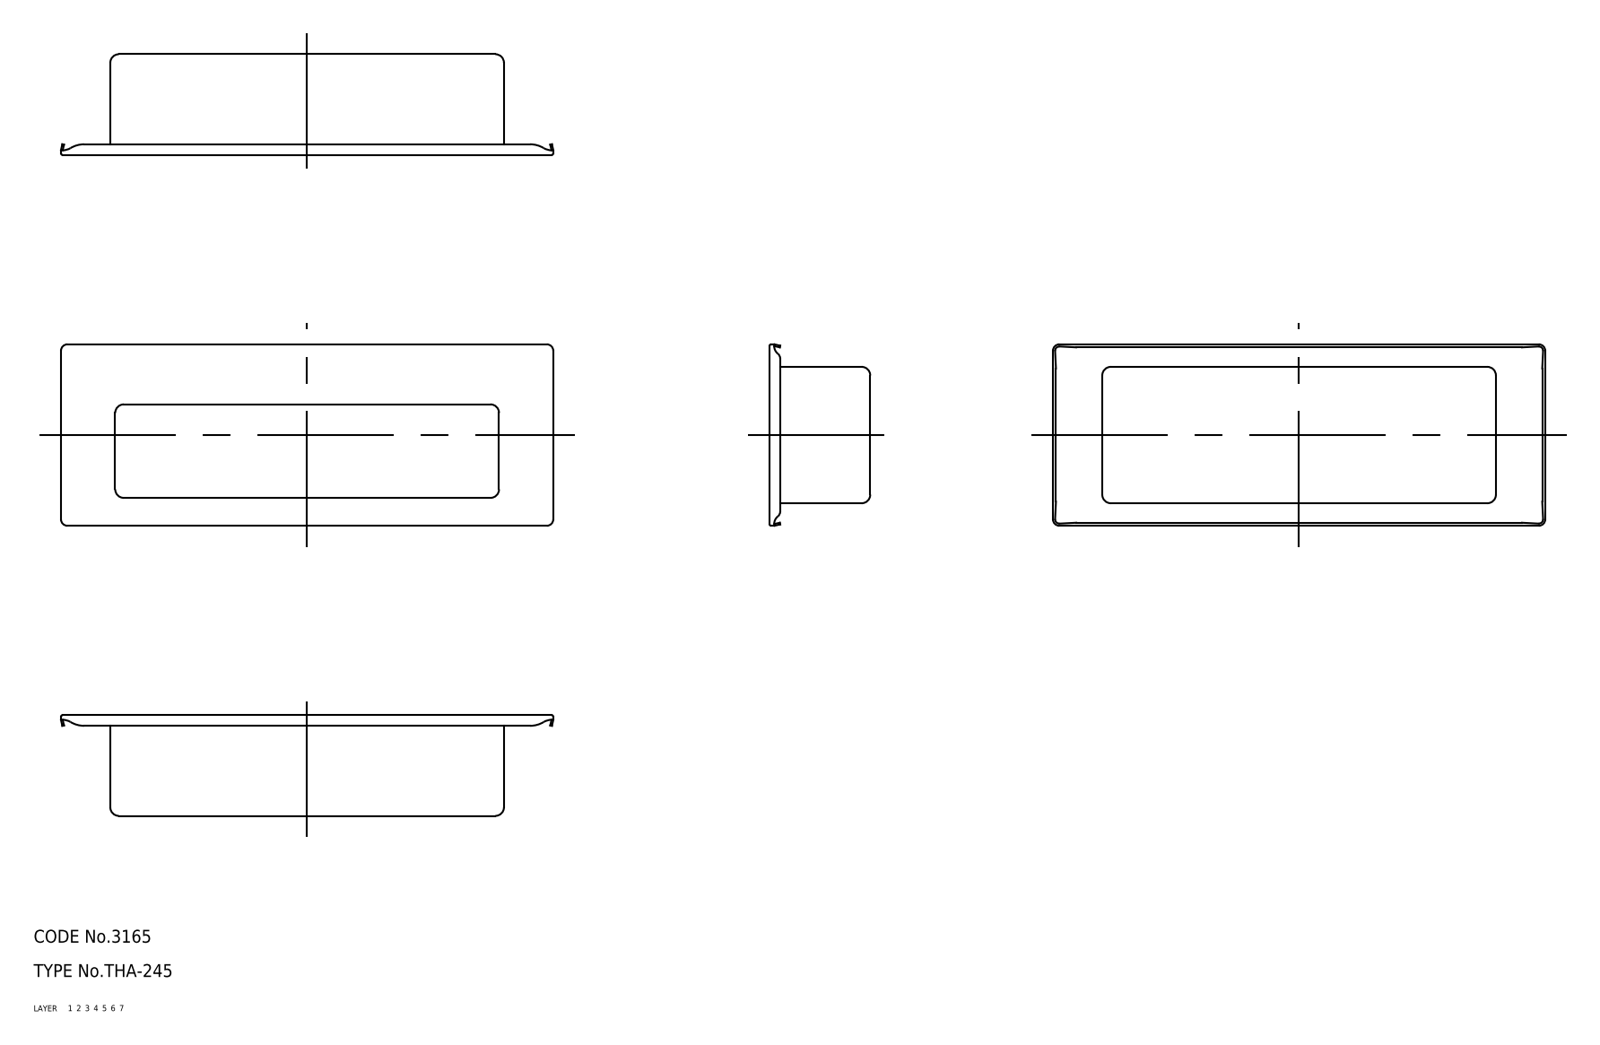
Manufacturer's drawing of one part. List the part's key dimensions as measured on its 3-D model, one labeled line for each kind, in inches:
Part name (STEP PRODUCT): 67115735; 67115748
STEP written by: CADfix (AUTOMOTIVE_DESIGN)
Units: inches
Bodies: 2 solids, 177 faces (0 planar, 0 cylindrical, 177 other)
Overall size (bounding box): 4.52 × 1.665 × 0.925
Volume: 0.53 in³ · Surface area: 45.32 in²
